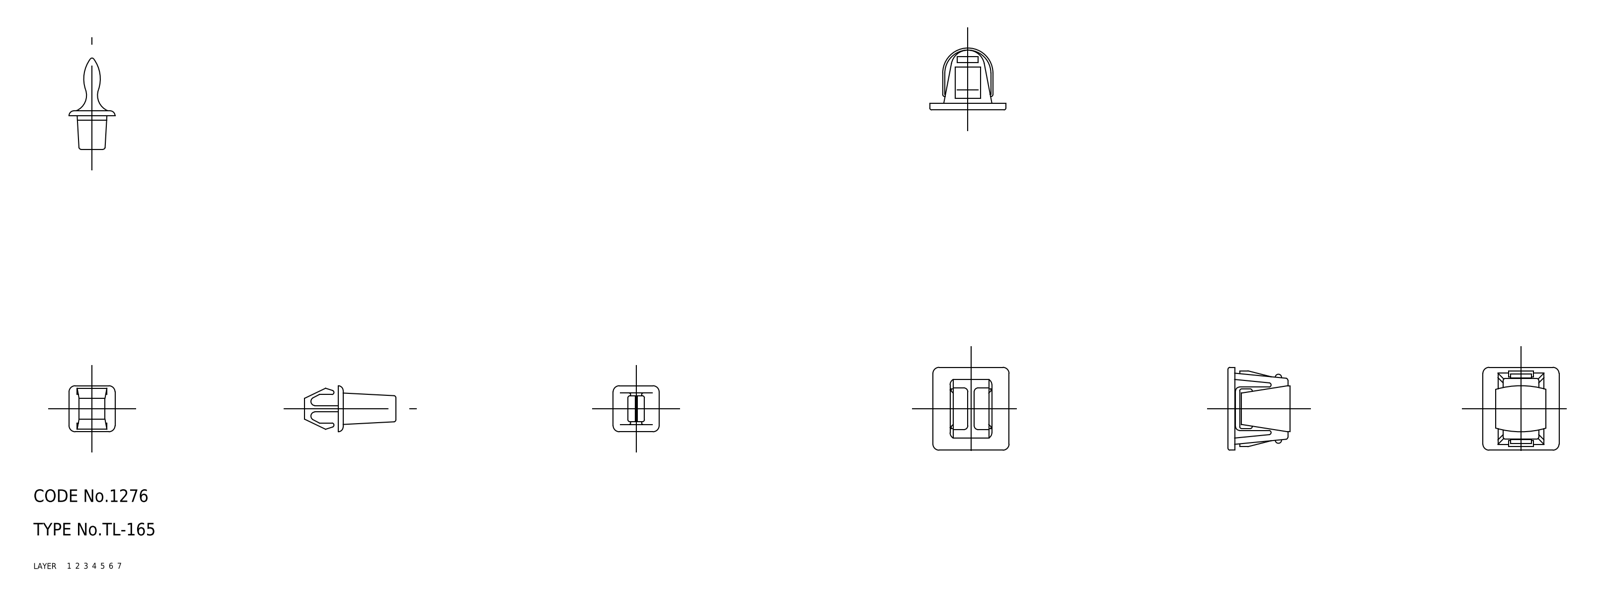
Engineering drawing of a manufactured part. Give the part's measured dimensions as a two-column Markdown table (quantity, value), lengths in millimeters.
| quantity | value |
| --- | --- |
| part name | leaf spring; keeper; base; TL_165_30091_36 |
| STEP written by | CADfix (AUTOMOTIVE_DESIGN) |
| units | millimeters |
| bodies | 3 solids, 178 faces (0 planar, 0 cylindrical, 178 other) |
| overall size | 52.32 × 19.8 × 18.2 |
| volume | 1 979 mm³ |
| surface area | 3 388 mm² |
